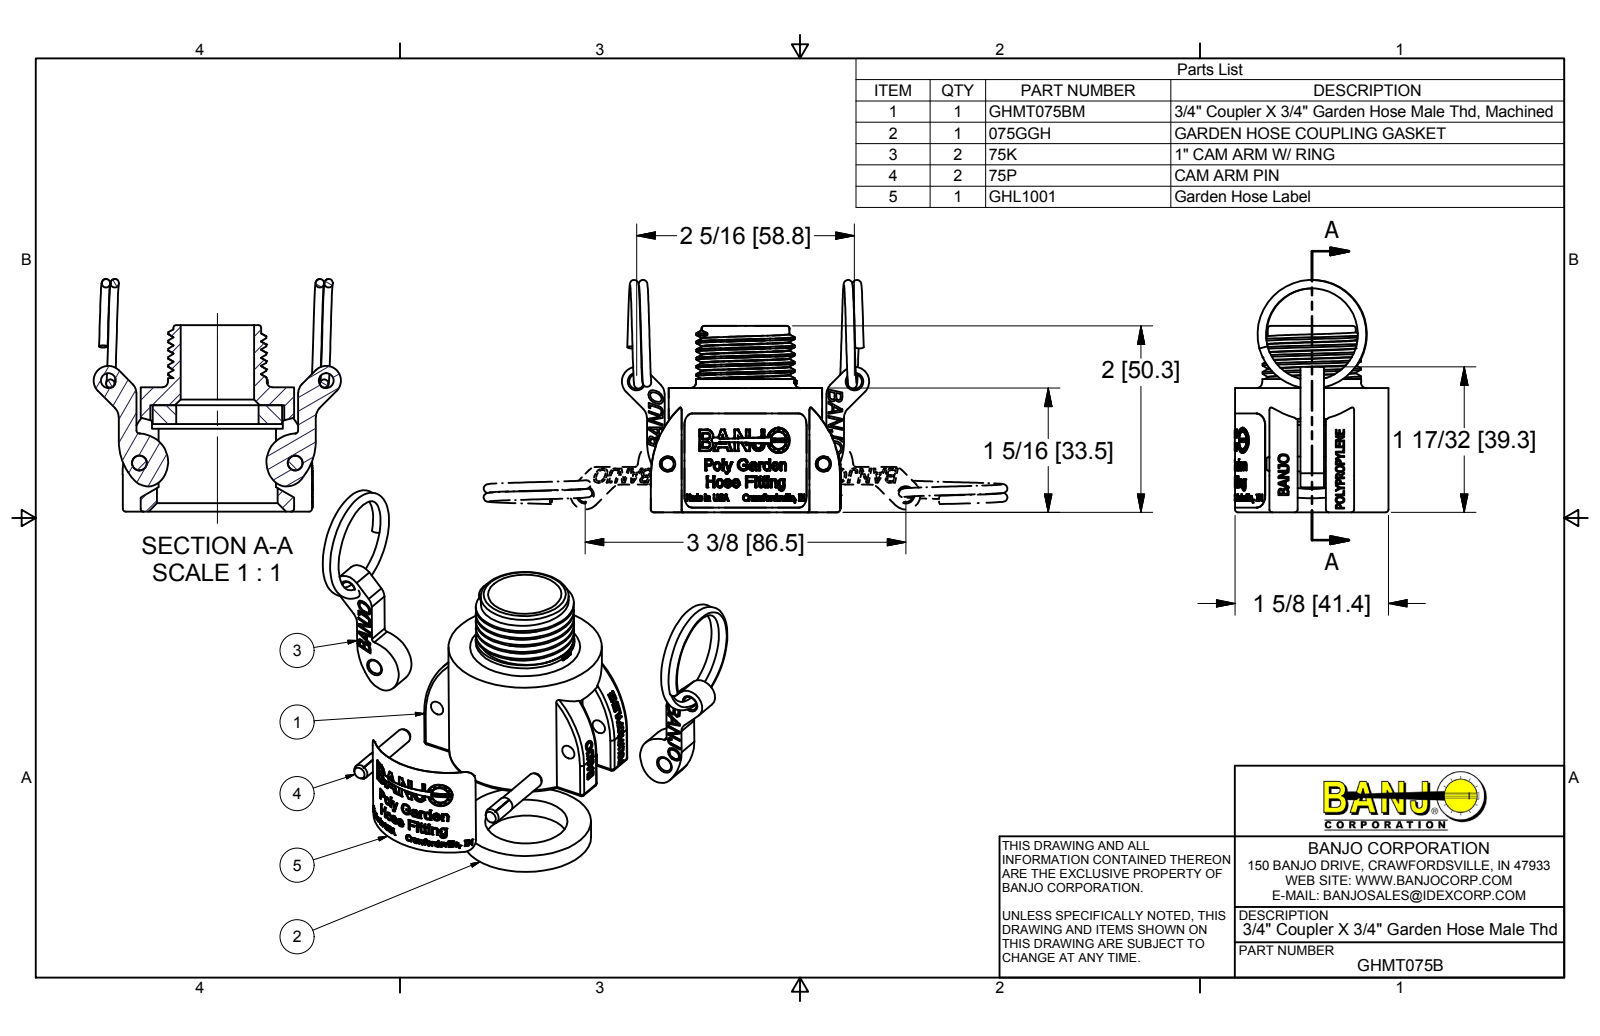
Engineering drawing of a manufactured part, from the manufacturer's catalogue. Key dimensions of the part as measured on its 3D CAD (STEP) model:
Part name (STEP PRODUCT): GHMT075BX; GHMT075BM; 075GGH; 75XK (+6 more)
STEP written by: Autodesk Inventor 2015 (AUTOMOTIVE_DESIGN)
Units: millimetres
Bodies: 8 solids, 1762 faces (818 planar, 189 cylindrical, 755 other)
Overall size (bounding box): 66.69 × 62.72 × 41.45
Volume: 7 815 mm³ · Surface area: 23 600 mm²
Round holes (diameter × count): ⌀3.96 ×4, ⌀4.04 ×2, ⌀19.81 ×1, ⌀22.22 ×1, ⌀32.61 ×1, ⌀36.12 ×1
Round bosses / shafts (diameter × count): ⌀4.17 ×2, ⌀41.4 ×1, ⌀34.92 ×1, ⌀26.67 ×1, ⌀26.5 ×1, ⌀23.72 ×1
Partial cylindrical surfaces — rounded edges, fillets, slot ends (radius × count): R0.79 ×16, R3.17 ×8, R3.97 ×2, R15.08 ×2, R25.4 ×2, R7.32 ×1, R13.59 ×1, R20.73 ×1
Main face-to-face distances: 7.62, 4.85, 6.35, 15.24, 5.08, 9.93, 0.51, 0.76, 23.6, 28.68
Hole centre spacings: 23.74, 55.1, 42.08, 58.76
